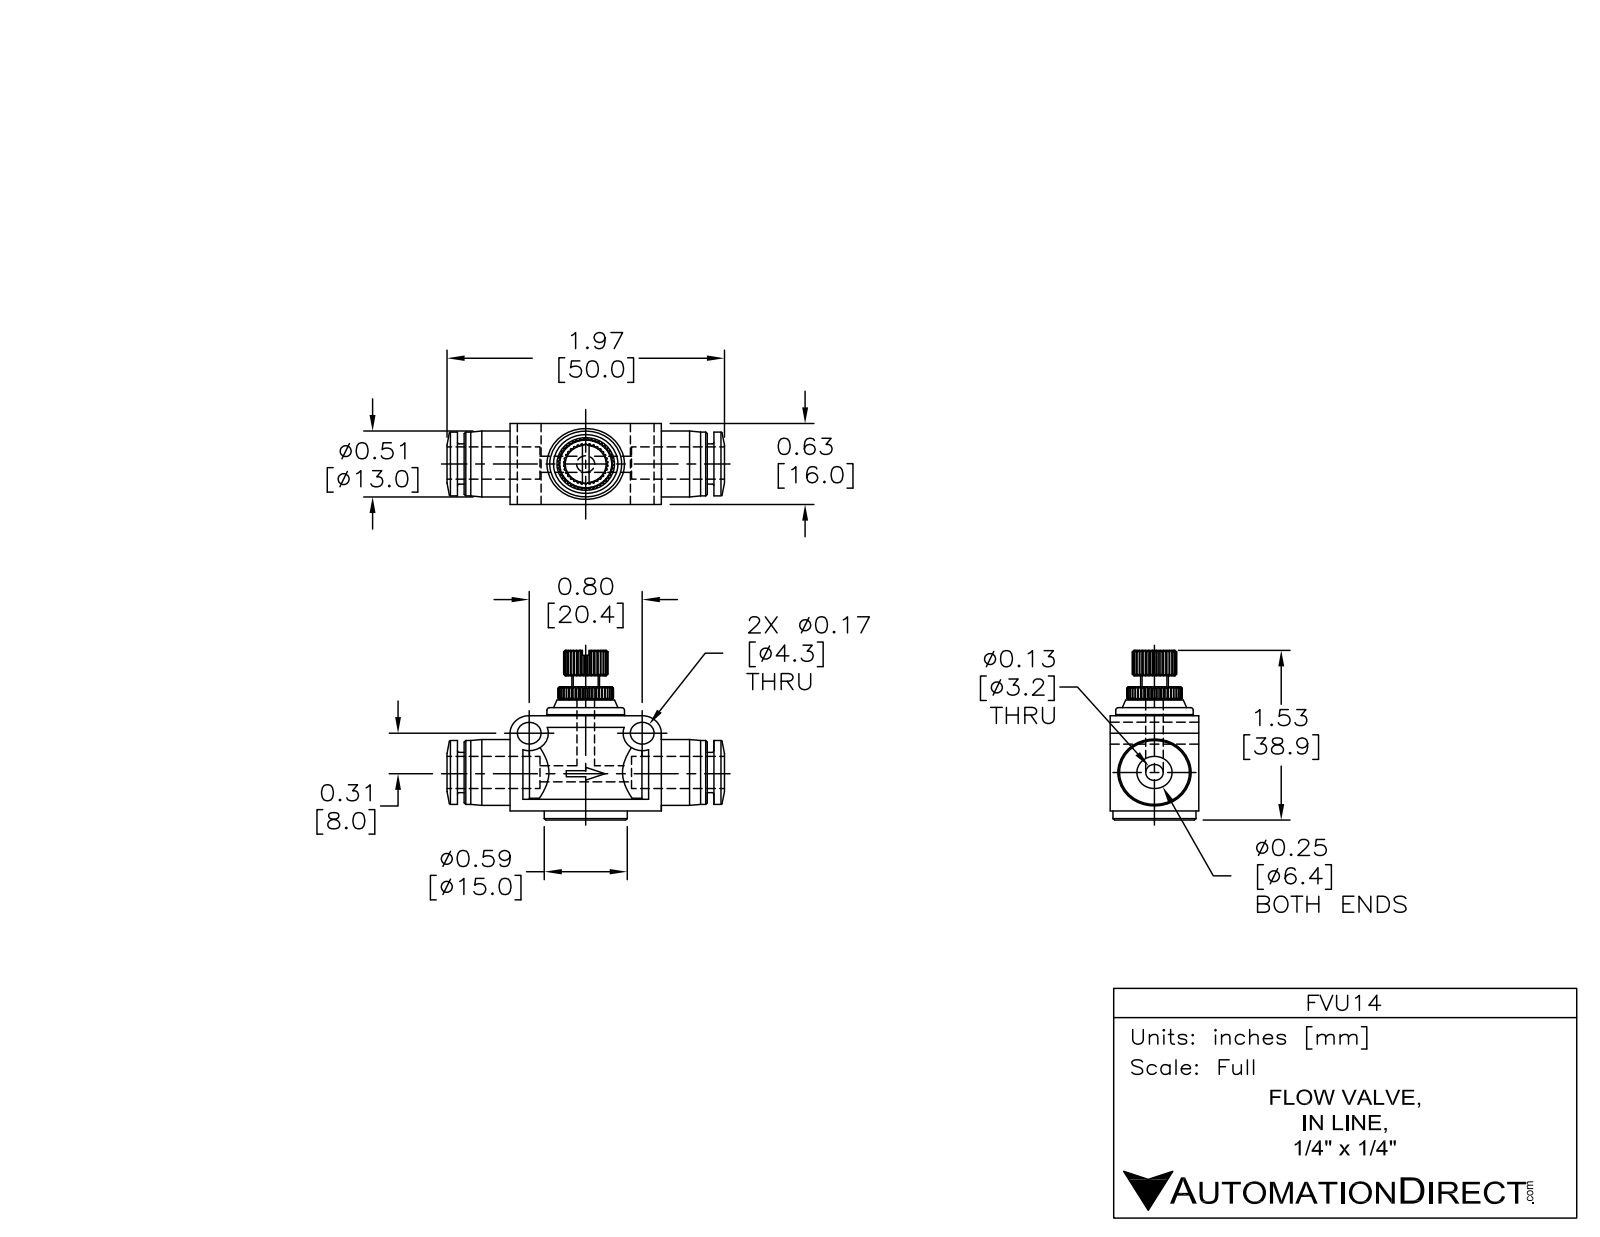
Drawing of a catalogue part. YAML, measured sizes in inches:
part_name: "FVU14"
step_written_by: "SolidWorks 2015 (AUTOMOTIVE_DESIGN)"
units: inches
bodies: {solids: 1, faces: 544, planar: 215, cylindrical: 133, other: 196}
overall_size: [1.972, 1.492, 0.63]
volume: 0.565
surface_area: 9.331
round_holes:
  - {diameter: 0.169, count: 2}
  - {diameter: 0.197, count: 1}
  - {diameter: 0.258, count: 1}
round_bosses_or_shafts:
  - {diameter: 0.591, count: 1}
  - {diameter: 0.551, count: 1}
  - {diameter: 0.551, count: 1}
  - {diameter: 0.512, count: 1}
  - {diameter: 0.496, count: 1}
  - {diameter: 0.313, count: 1}
  - {diameter: 0.236, count: 1}
  - {diameter: 0.197, count: 1}
partial_cylinders:
  - {radius: 0.136, count: 2}
  - {radius: 0.157, count: 1}
  - {radius: 0.197, count: 1}
  - {radius: 0.209, count: 1}
  - {radius: 0.335, count: 1}
face_to_face_distances: [0.091, 0.63, 0.622, 0.74, 0.071, 0.811, 0.65, 0.161, 0.374, 0.047]
hole_center_spacings: [0.803]
